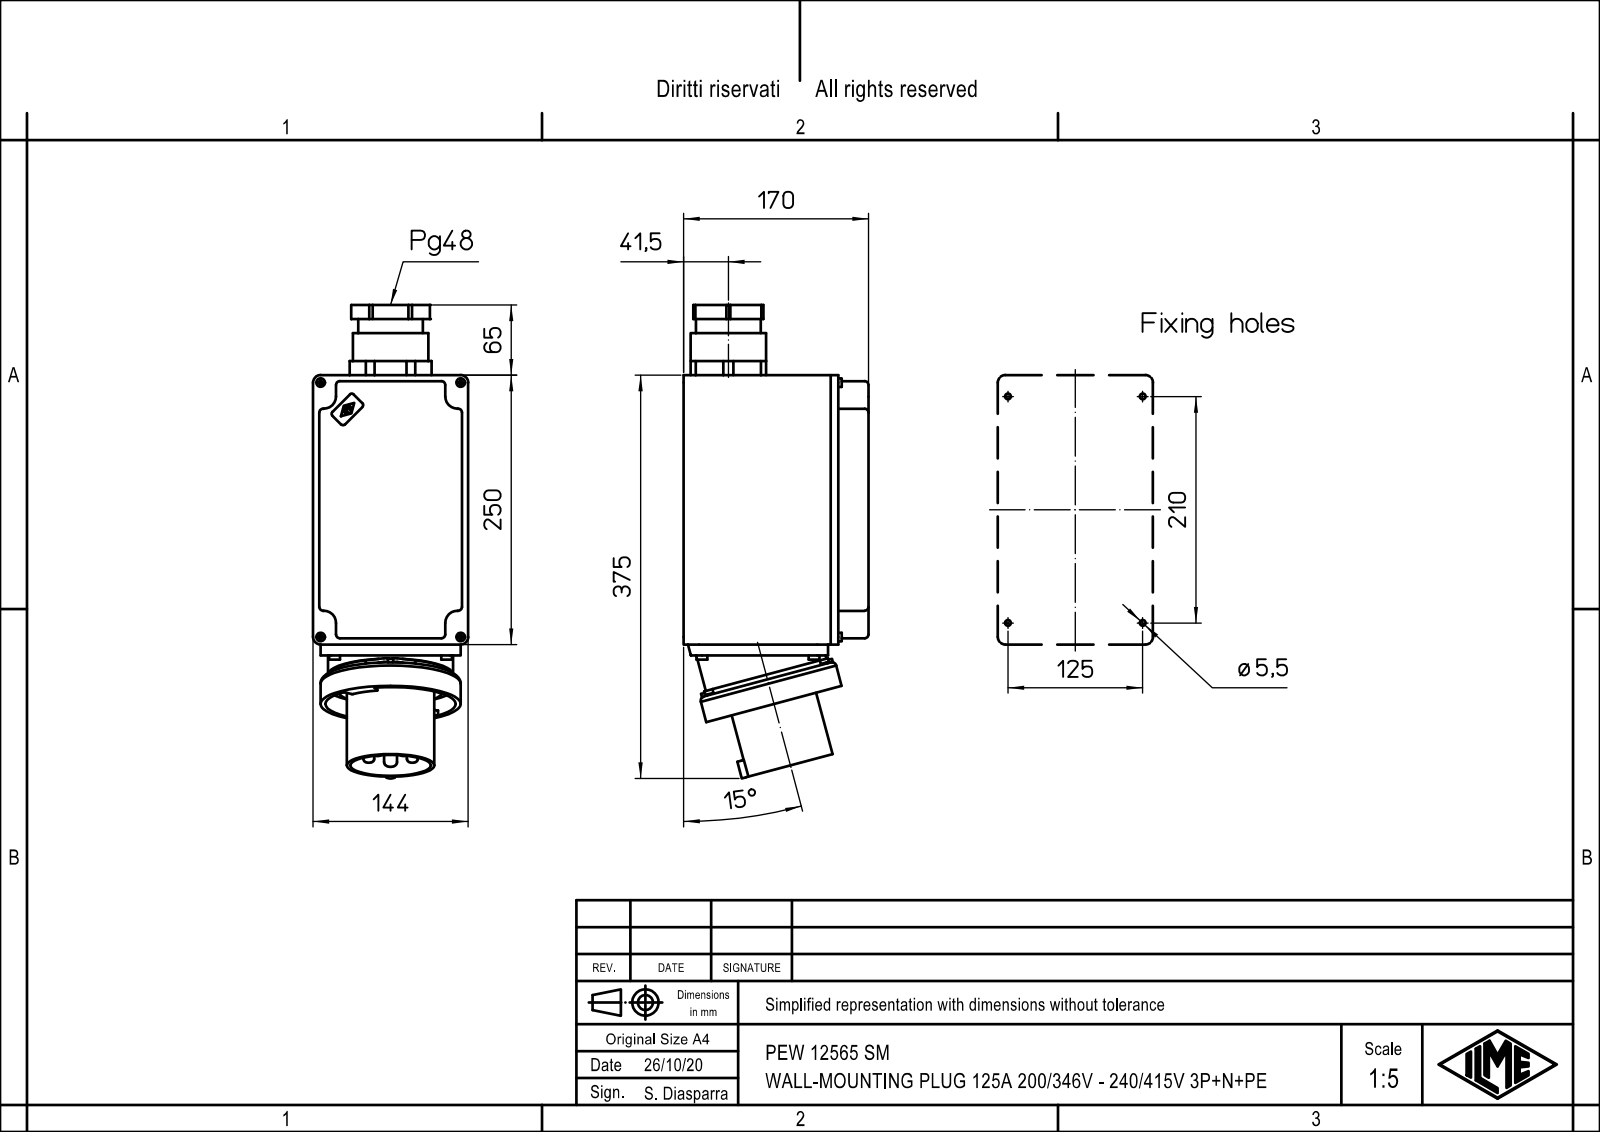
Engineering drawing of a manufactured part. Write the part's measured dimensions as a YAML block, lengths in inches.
part_name: "PEW_12565_SM"
step_written_by: "Creo Elements/Direct Modeling 20.1B 02-Apr-2019 (C) Parametric Technology GmbH (AUTOMOTIVE_DESIGN)"
units: inches
bodies: {solids: 1, faces: 486, planar: 270, cylindrical: 172, other: 44}
overall_size: [17.348, 8.98, 5.669]
volume: 420.9
surface_area: 489.8
round_holes:
  - {diameter: 0.197, count: 4}
  - {diameter: 0.213, count: 4}
  - {diameter: 0.256, count: 4}
  - {diameter: 1.89, count: 1}
  - {diameter: 2.941, count: 1}
  - {diameter: 4.469, count: 1}
  - {diameter: 4.764, count: 1}
round_bosses_or_shafts:
  - {diameter: 0.394, count: 8}
  - {diameter: 0.315, count: 4}
  - {diameter: 0.197, count: 2}
  - {diameter: 5.118, count: 1}
  - {diameter: 4.685, count: 1}
  - {diameter: 4.567, count: 1}
  - {diameter: 4.449, count: 1}
  - {diameter: 3.819, count: 1}
partial_cylinders:
  - {radius: 0.138, count: 16}
  - {radius: 0.013, count: 15}
  - {radius: 0.039, count: 8}
  - {radius: 0.157, count: 5}
  - {radius: 0.098, count: 4}
  - {radius: 0.197, count: 4}
  - {radius: 0.276, count: 4}
  - {radius: 0.394, count: 4}
face_to_face_distances: [5.669, 6.751, 5.648, 1.103, 10.237, 5.443, 0.226, 0.226, 5.217, 5.443]
hole_center_spacings: [4.094, 2.262, 3.741, 4.921, 5.791, 8.268, 9.622]
